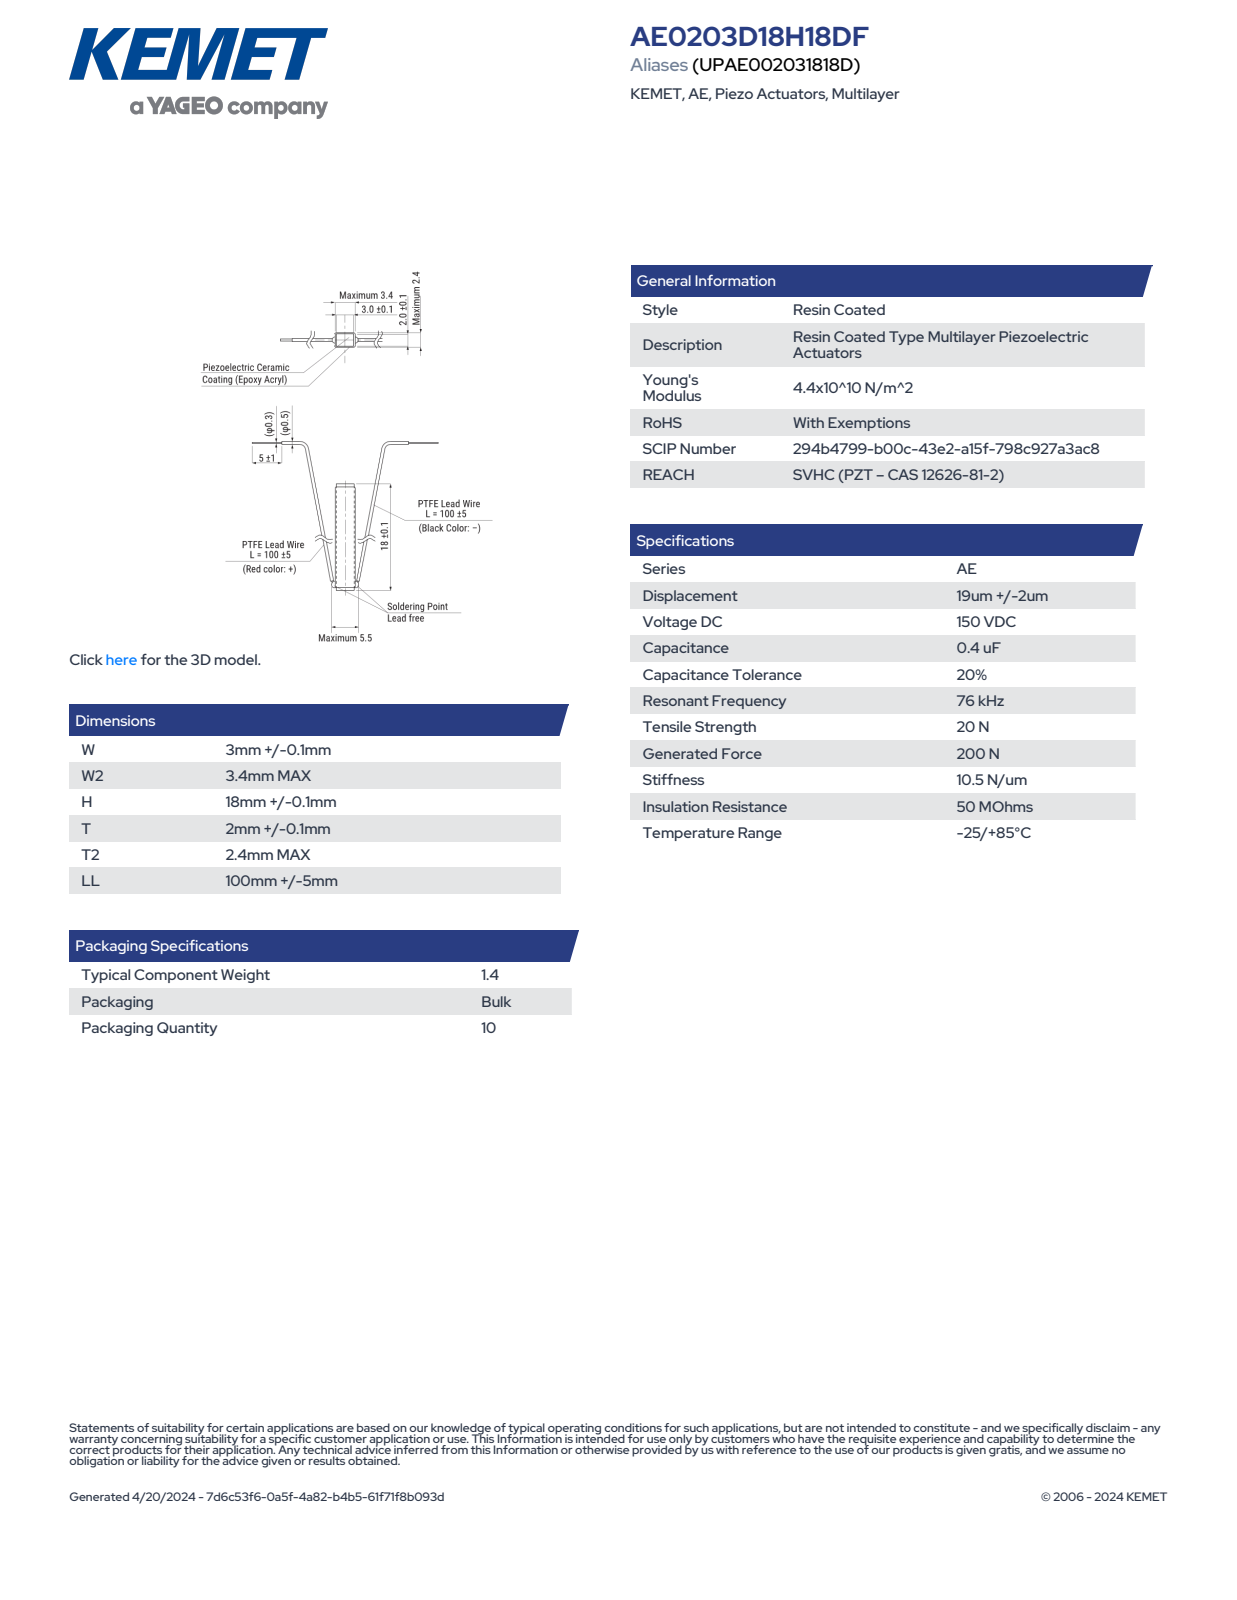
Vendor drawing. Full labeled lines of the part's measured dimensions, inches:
Part name (STEP PRODUCT): AL_KAE1_W3.1W23.4H18.1T2.1T22.4
STEP written by: SolidWorks 2014 (AUTOMOTIVE_DESIGN)
Units: inches
Bodies: 4 solids, 93 faces (85 planar, 8 cylindrical, 0 other)
Overall size (bounding box): 0.713 × 0.134 × 0.094
Volume: 0.007 in³ · Surface area: 0.326 in²
Partial cylindrical surfaces — rounded edges, fillets, slot ends (radius × count): R0.006 ×8
Main face-to-face distances: 0.089, 0.118, 0.083, 0.114, 0.094, 0.122, 0.713, 0.287, 0.426, 0.07
